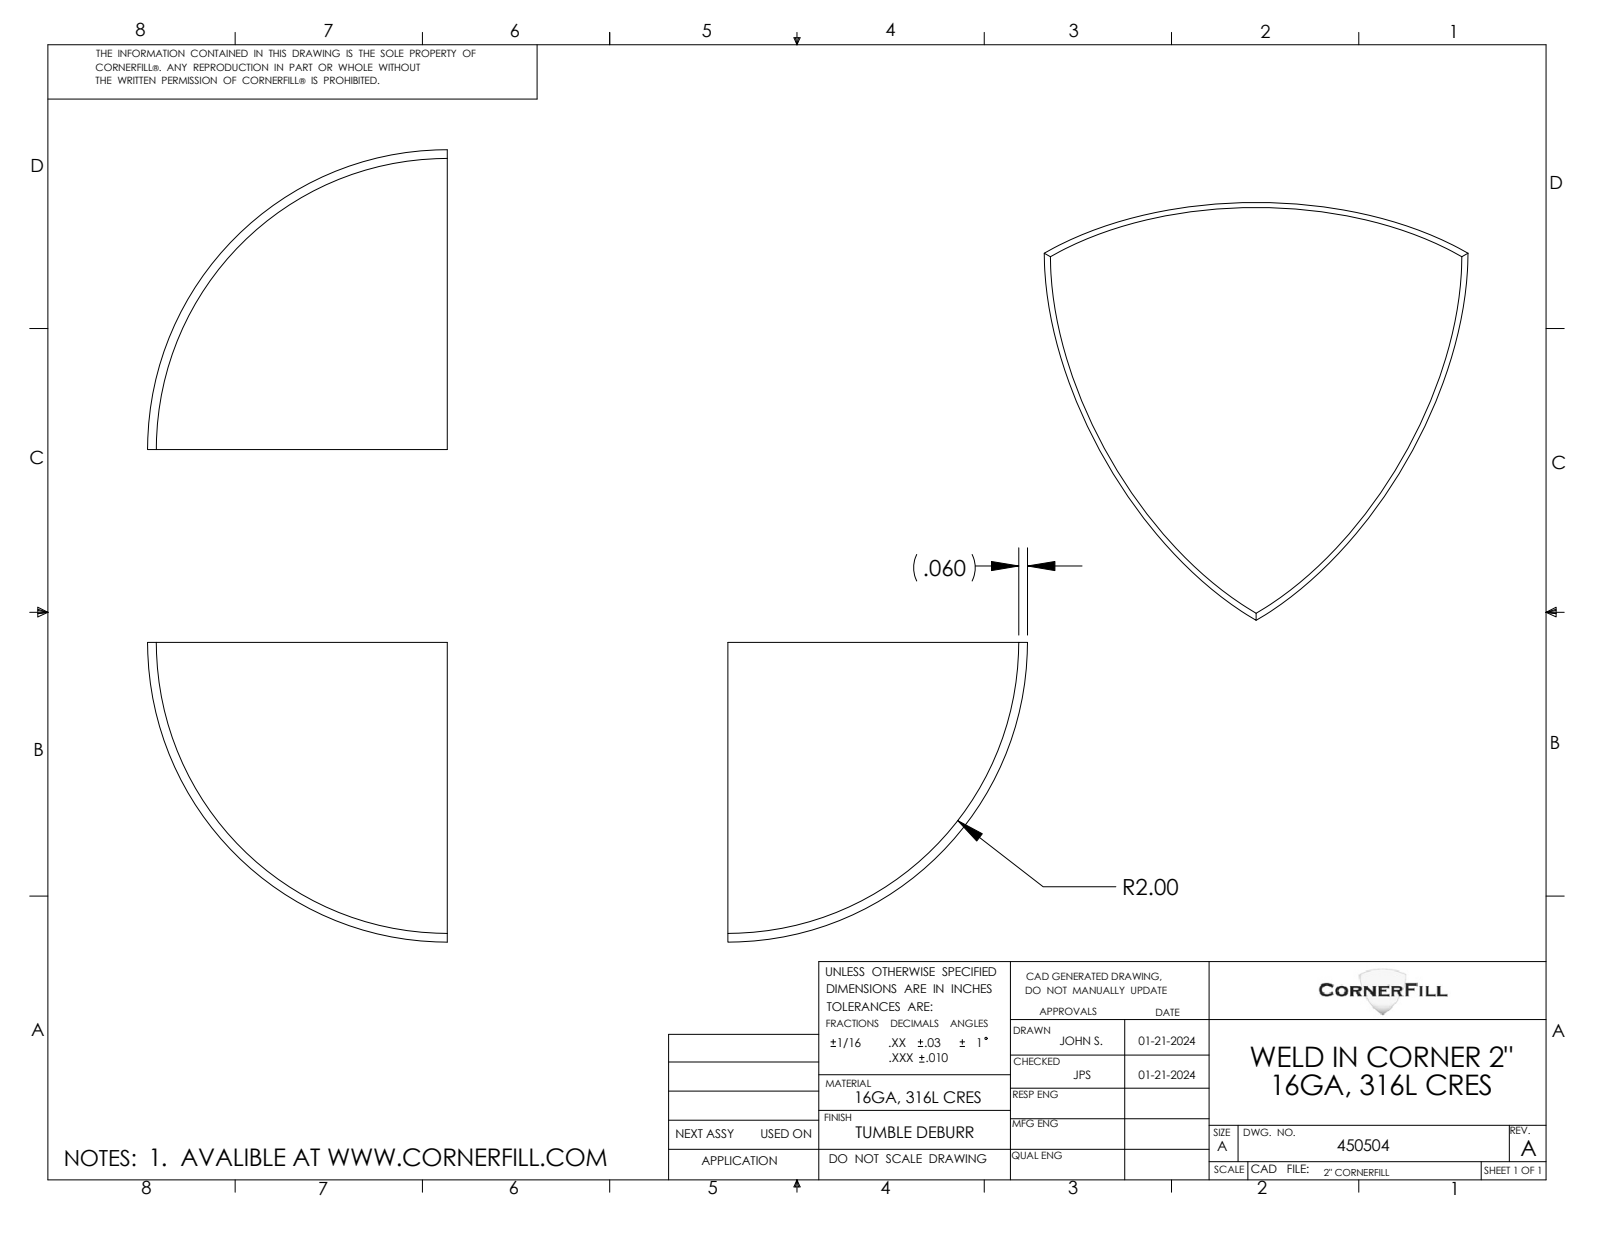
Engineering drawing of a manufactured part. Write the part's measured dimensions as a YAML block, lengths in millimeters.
part_name: "450504"
step_written_by: "SolidWorks 2021 (CONFIG_CONTROL_DESIGN)"
units: millimeters
bodies: {solids: 1, faces: 5, planar: 3, cylindrical: 0, other: 2}
overall_size: [74, 52.3, 52.3]
volume: 6360
surface_area: 8723
